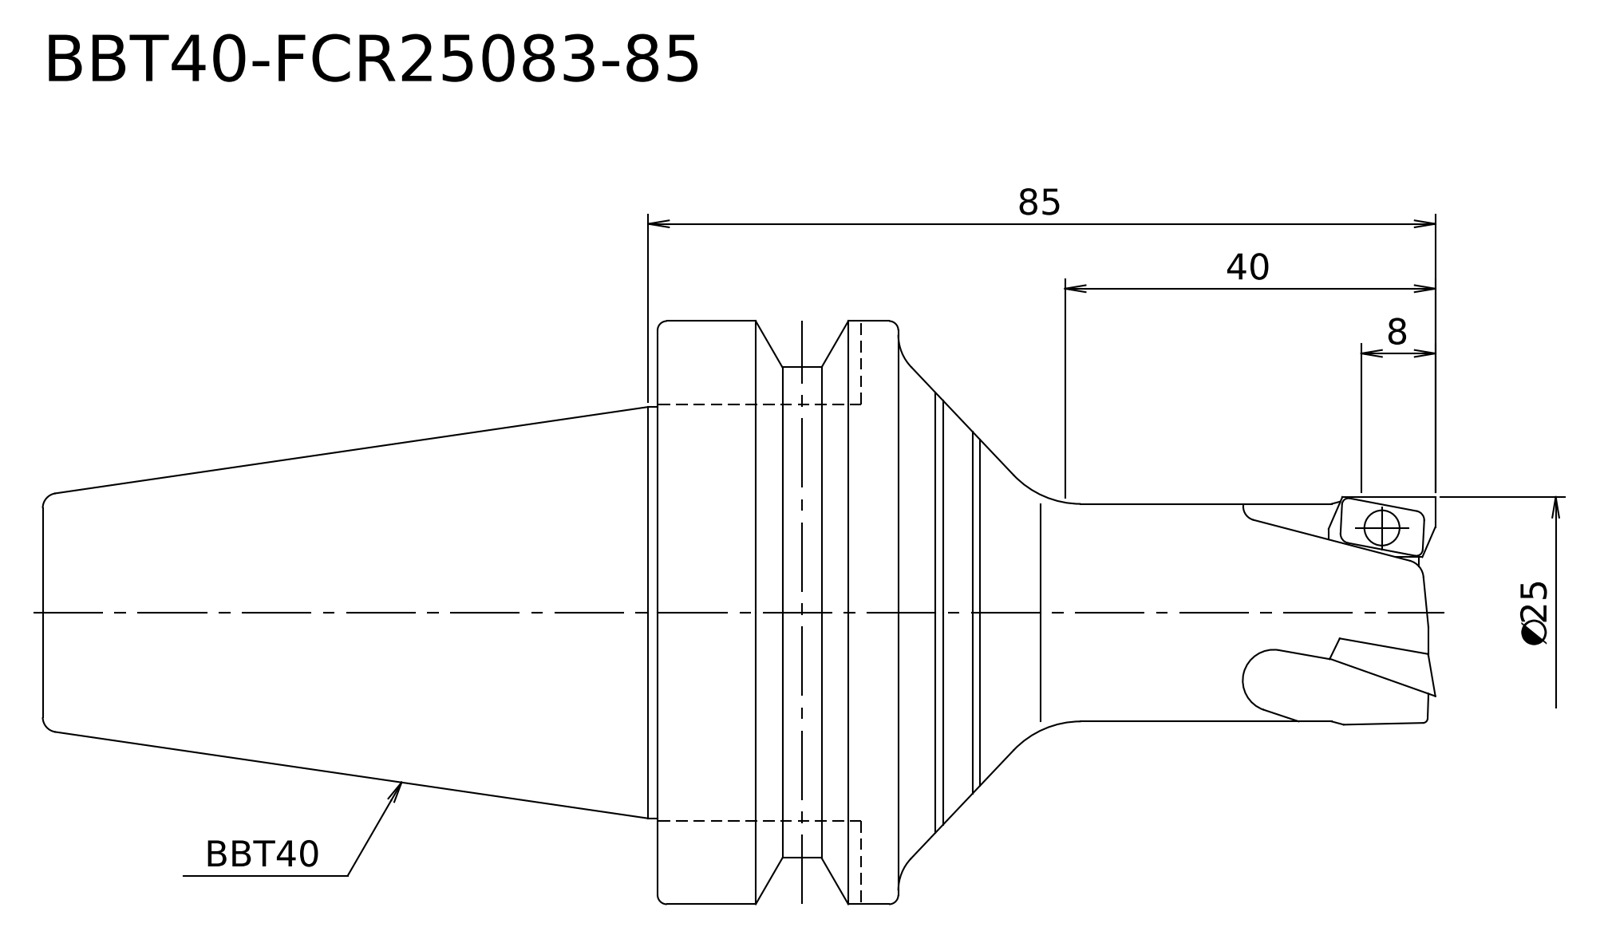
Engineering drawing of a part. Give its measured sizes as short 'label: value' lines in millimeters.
written by: Kubotek KeyCreator V8.5.1 (14335) (CONFIG_CONTROL_DESIGN)
unit: mm
bodies: 1 solid, 17 faces (4 planar, 6 cylindrical, 7 other)
size: 150.4 × 63 × 63
volume: 180 215 mm³; area: 22 507 mm²
bosses: 1× ⌀63, 1× ⌀53, 1× ⌀44.45, 1× ⌀25, 1× ⌀23.5
face distances: 66.4, 84, 150.4, 58, 26, 92.4
